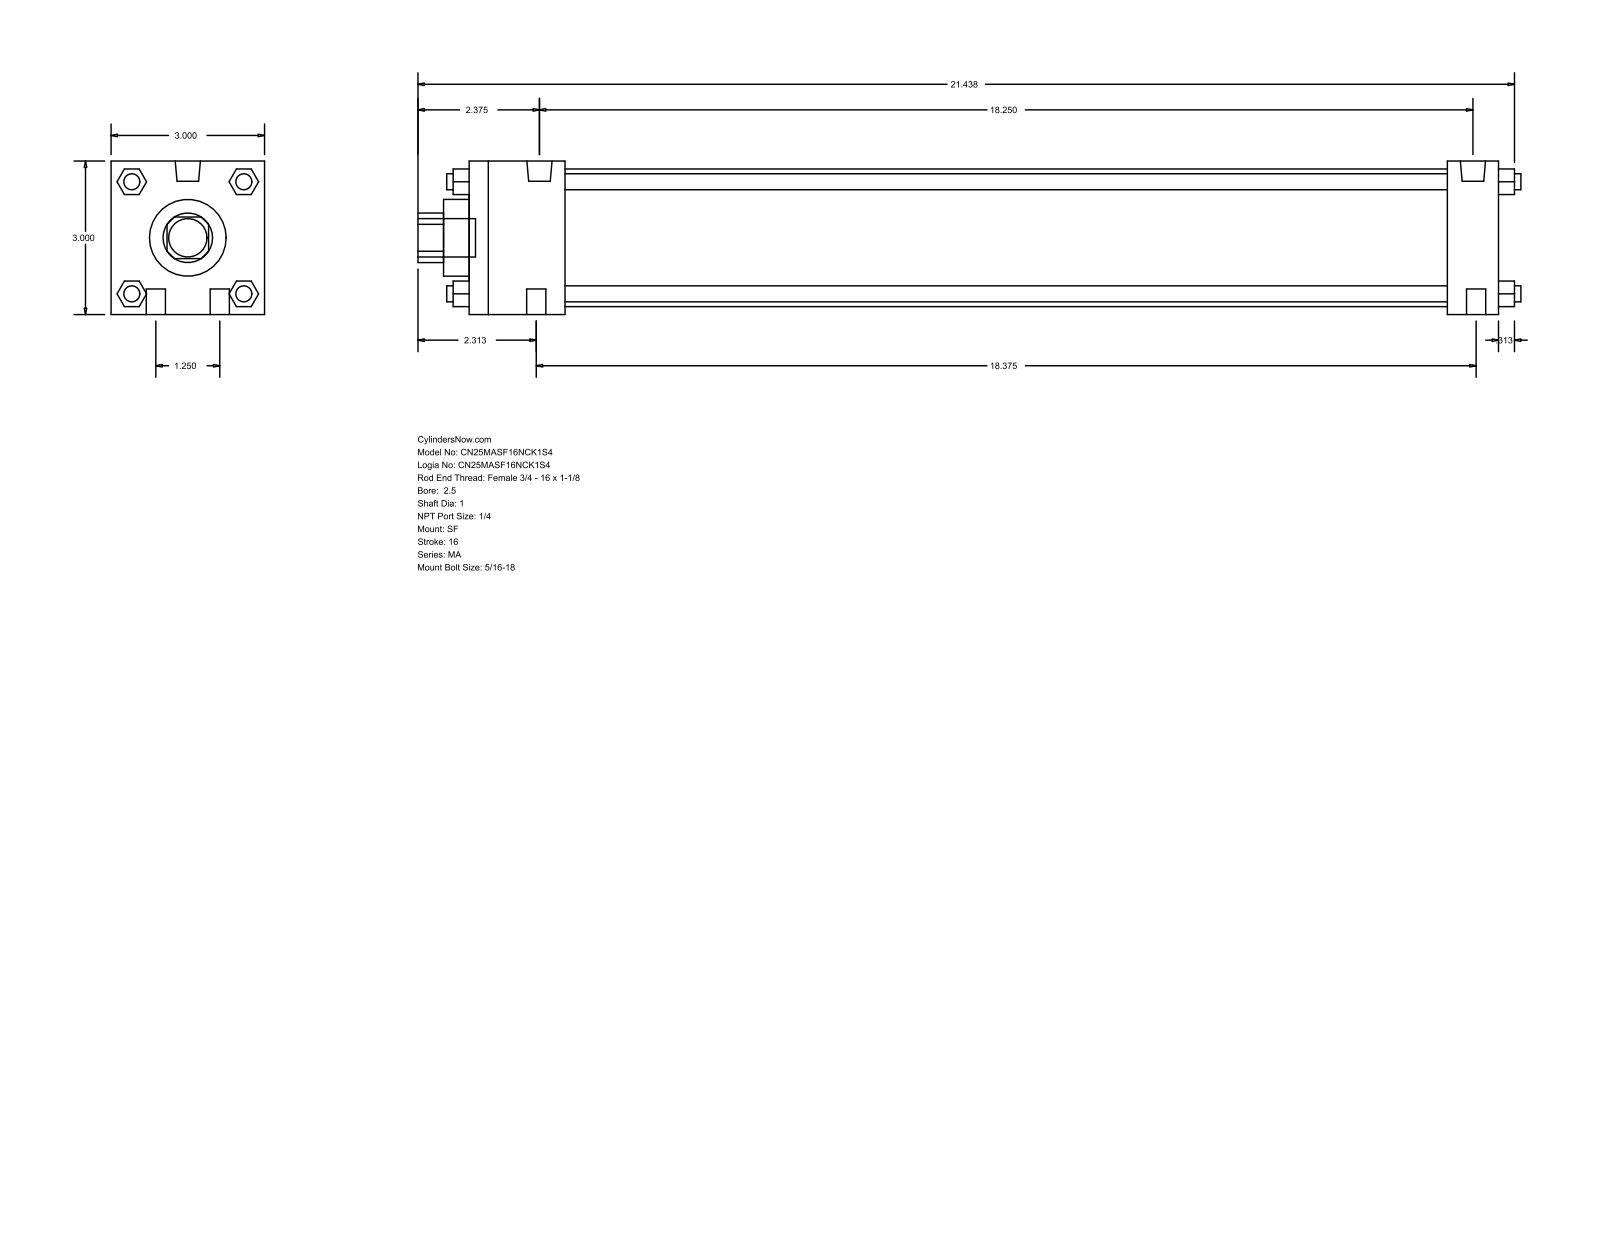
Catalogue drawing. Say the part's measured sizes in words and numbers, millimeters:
The part is named "MA_SF__0250_1". Its 3-D file was written by "GSSL Pune (CONFIG_CONTROL_DESIGN)". It is 0 solids with 124 faces: 94 planar, 30 cylindrical and 0 other. Overall it measures 547.69 by 76.2 by 76.2 millimeters. Round holes: 1 of diameter 25.4, 1 of diameter 38.1, 1 of diameter 68.33. Round bosses or shafts: 6 of diameter 7.94, 4 of diameter 9.53, 2 of diameter 12.49, 1 of diameter 19.05. Partial cylindrical surfaces (rounded edges, fillets, slot ends): 1 of radius 12.29. The main face-to-face distances are 76.2, 511.18, 12.7, 25.4, 485.78, 47.63, 438.15, 463.55, 27.81, 48.17.
